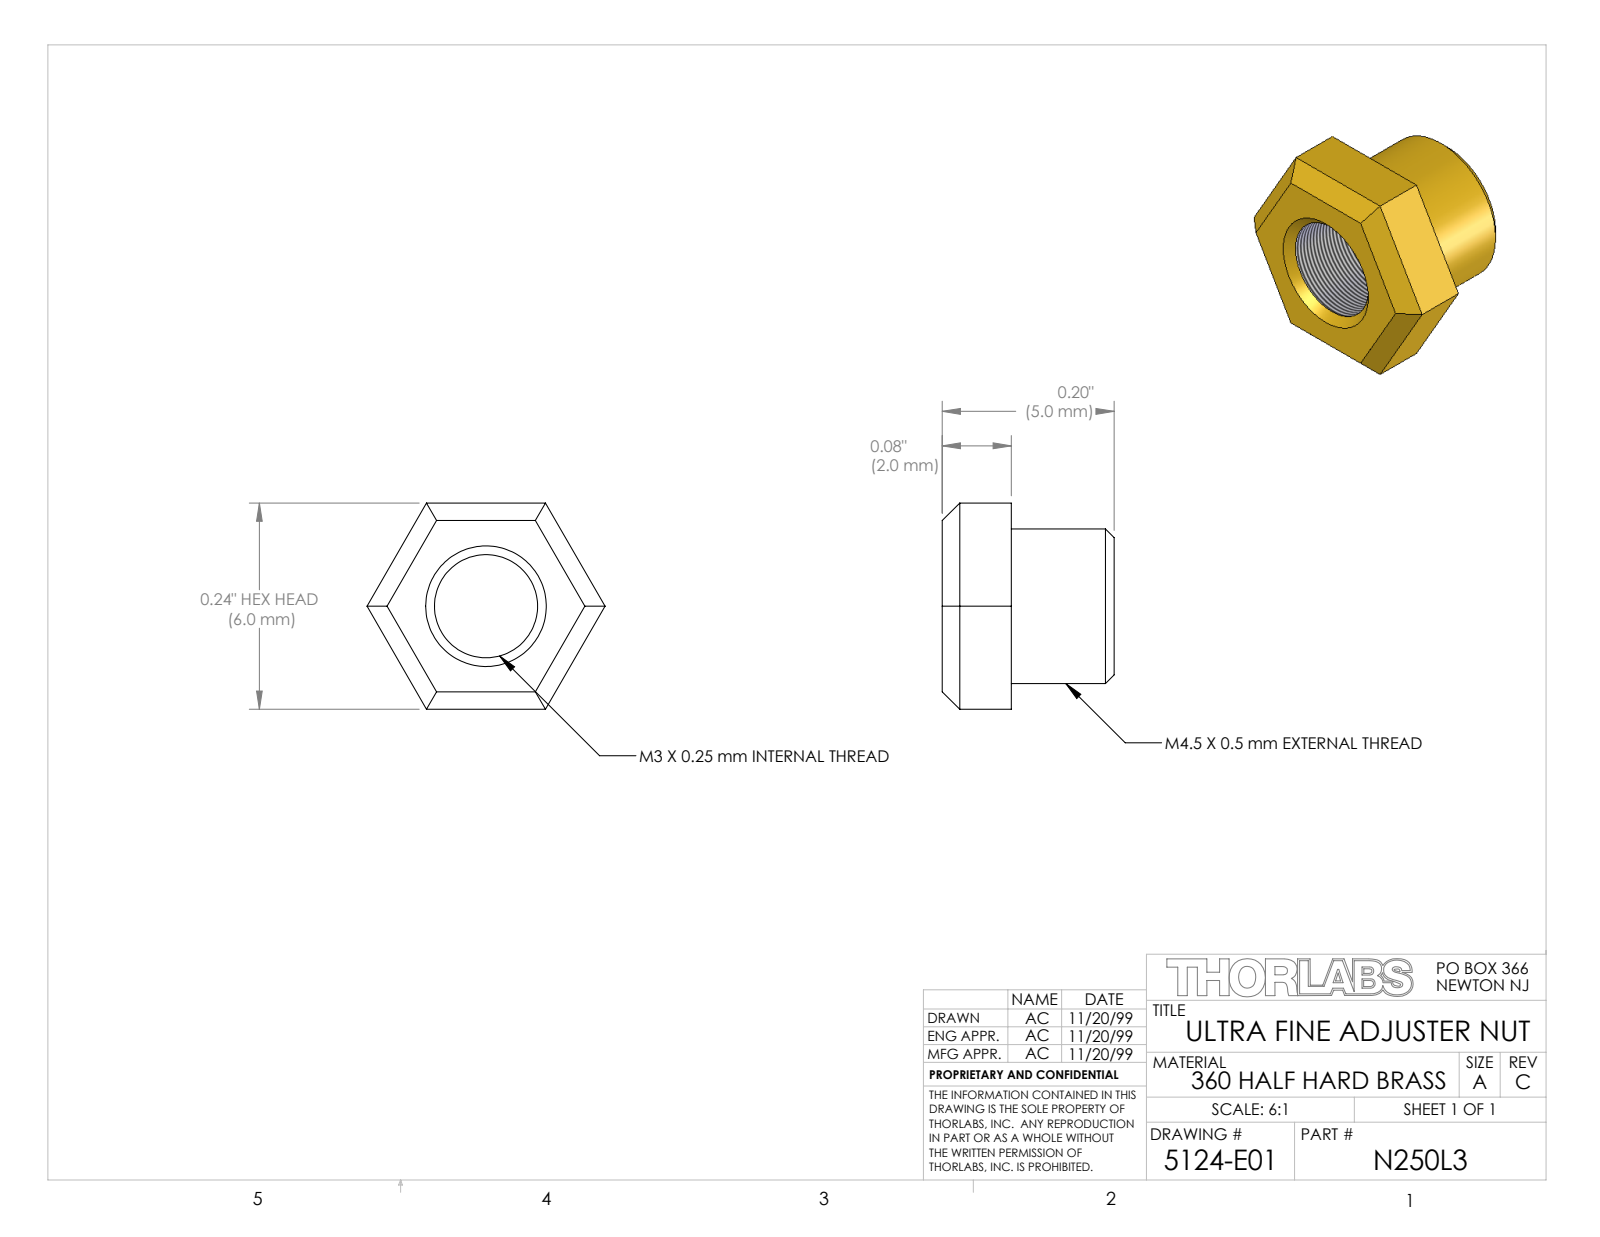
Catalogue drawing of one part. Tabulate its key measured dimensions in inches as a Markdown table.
| quantity | value |
| --- | --- |
| part name | 5124-E0W |
| STEP written by | SolidWorks 2007 (AUTOMOTIVE_DESIGN) |
| units | inches |
| bodies | 1 solid, 20 faces (10 planar, 6 cylindrical, 4 other) |
| overall size | 0.25 × 0.219 × 0.197 |
| volume | 0.004 in³ |
| surface area | 0.26 in² |
| round holes (diameter × count) | 0.118 × 1 |
| round bosses / shafts (diameter × count) | 0.178 × 1, 0.158 × 1 |
| main face-to-face distances | 0.217, 0.079, 0.118, 0.197, 0.108, 0.089 |
